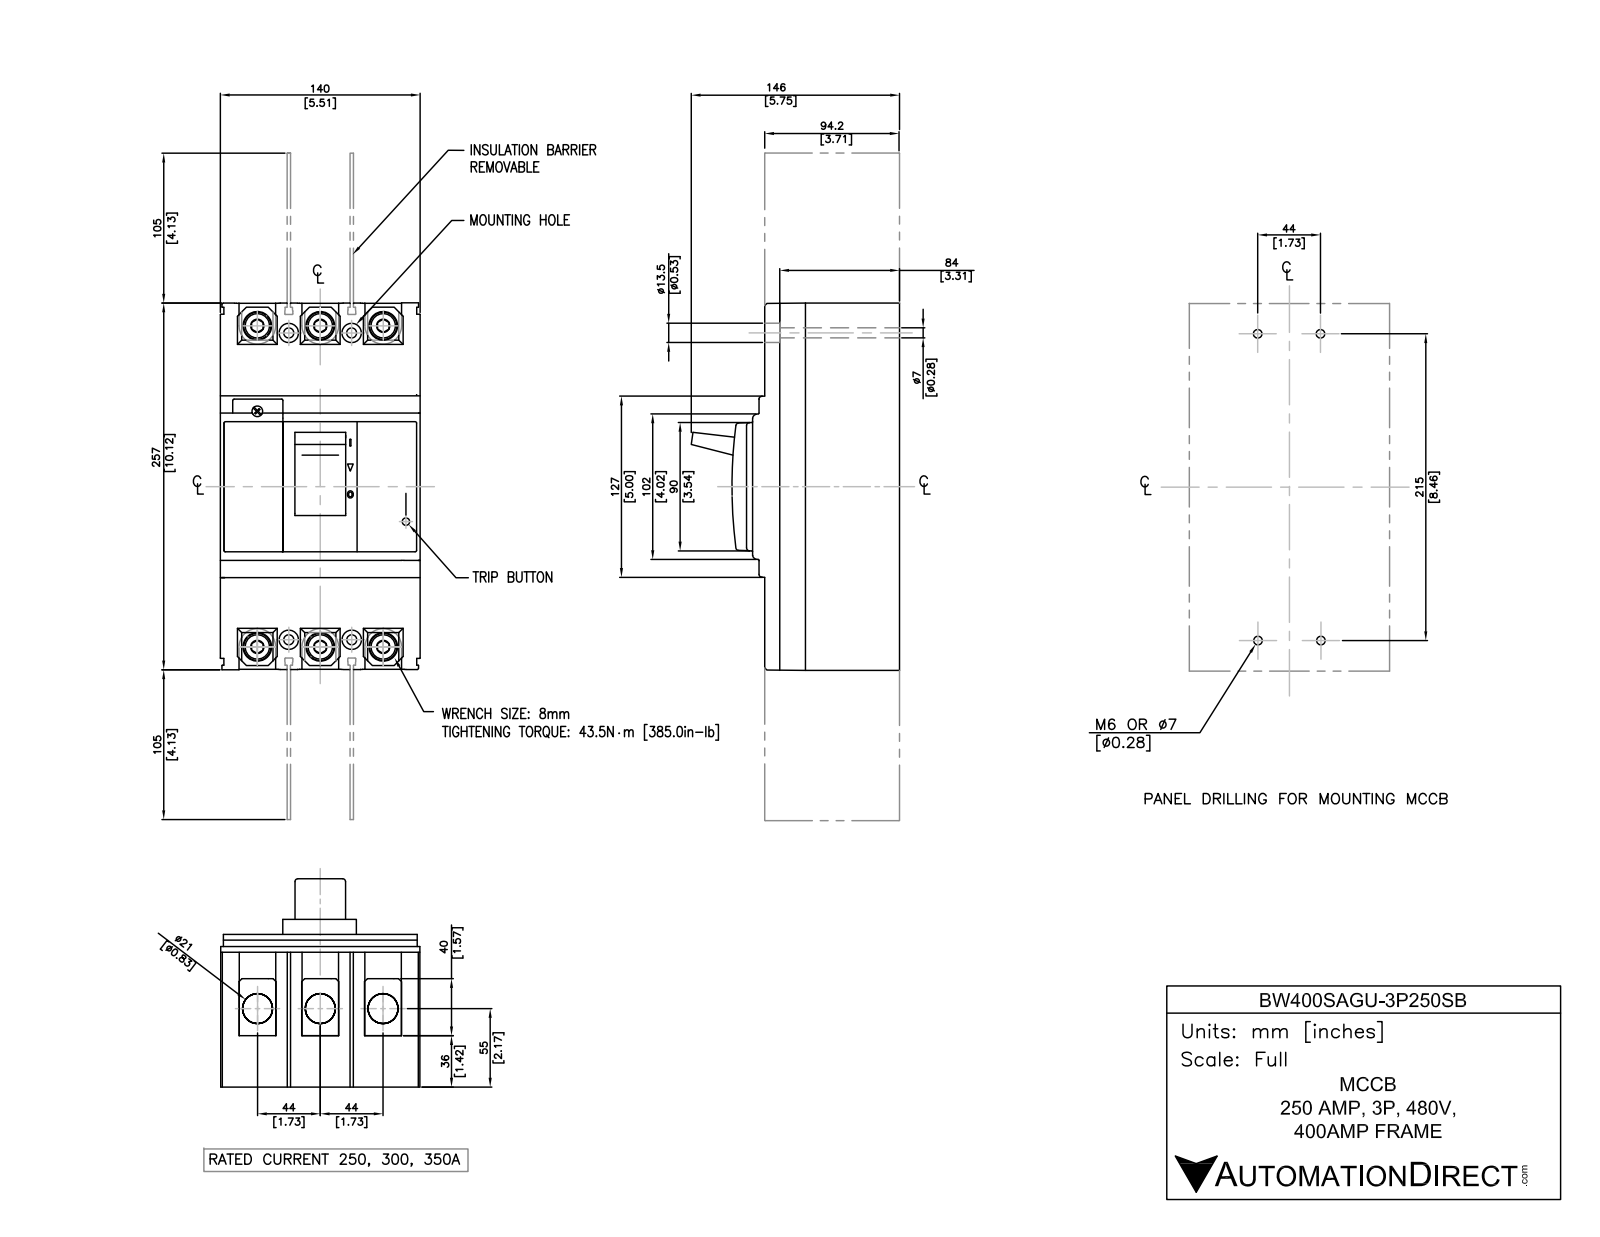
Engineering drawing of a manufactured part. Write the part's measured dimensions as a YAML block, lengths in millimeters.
part_name: "BW400SAGU-3P250SB"
step_written_by: "SolidWorks 2018 (AUTOMOTIVE_DESIGN)"
units: millimeters
bodies: {solids: 18, faces: 382, planar: 320, cylindrical: 62, other: 0}
overall_size: [340, 148.3, 140]
volume: 3368000
surface_area: 253400
round_holes:
  - {diameter: 7, count: 4}
  - {diameter: 10.5, count: 4}
  - {diameter: 12, count: 4}
  - {diameter: 12.5, count: 4}
  - {diameter: 13.5, count: 4}
round_bosses_or_shafts:
  - {diameter: 10, count: 4}
partial_cylinders:
  - {radius: 12.8, count: 6}
face_to_face_distances: [140, 44, 8, 94.5, 32, 58.5, 36, 10, 50.5, 12.5]
hole_center_spacings: [22.6, 43, 57.6, 66.2, 91, 108.6, 221.1, 229.7]
